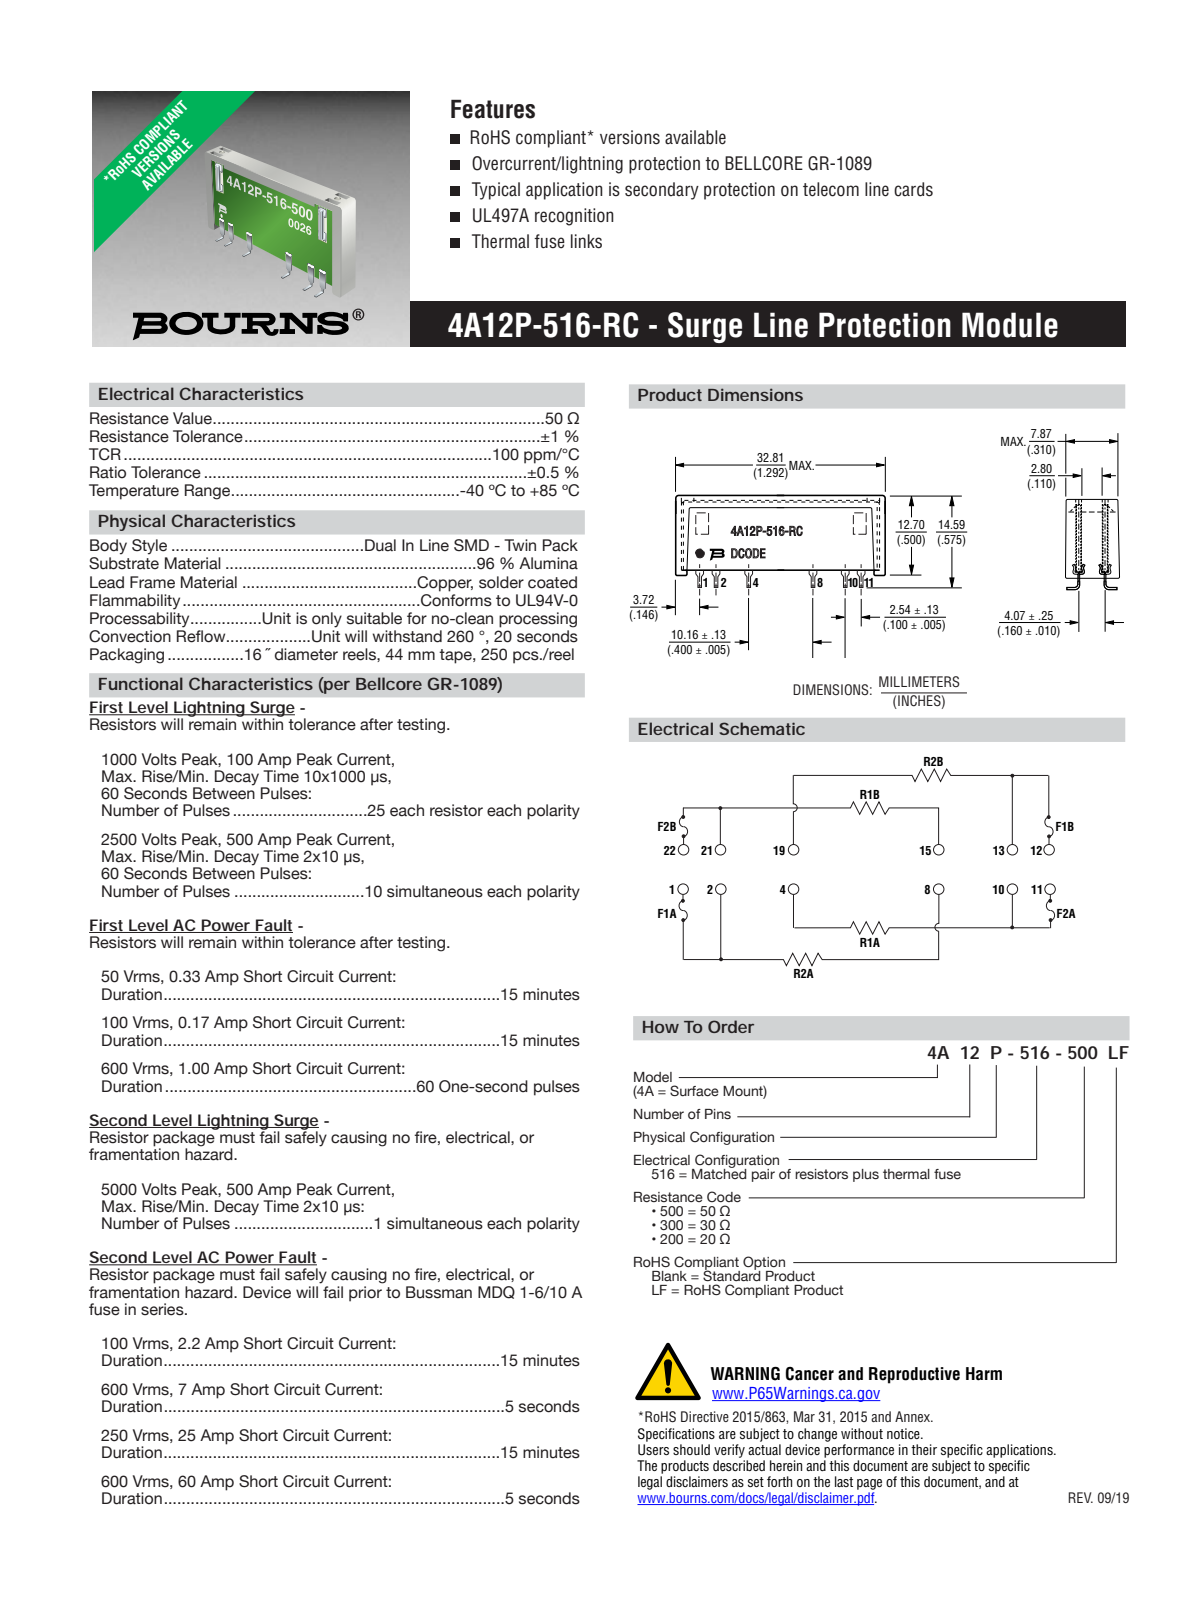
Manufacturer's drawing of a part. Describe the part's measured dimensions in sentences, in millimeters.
The part is named "4A12P-516-500". Its 3-D file was written by "PRO/ENGINEER BY PARAMETRIC TECHNOLOGY CORPORATION, 2010100 (CONFIG_CONTROL_DESIGN)". It is 1 solid with 130 faces: 98 planar, 32 cylindrical and 0 other. Overall it measures 32.81 by 14.59 by 8 millimeters. Its volume is 3 149 cubic millimeters and its surface area 1 612 square millimeters. Partial cylindrical surfaces (rounded edges, fillets, slot ends): 10 of radius 0.63. The main face-to-face distances are 7.46, 12.7, 7.67, 32.82, 7.88, 0.5, 11.34, 1.36, 1.89, 13.23.
